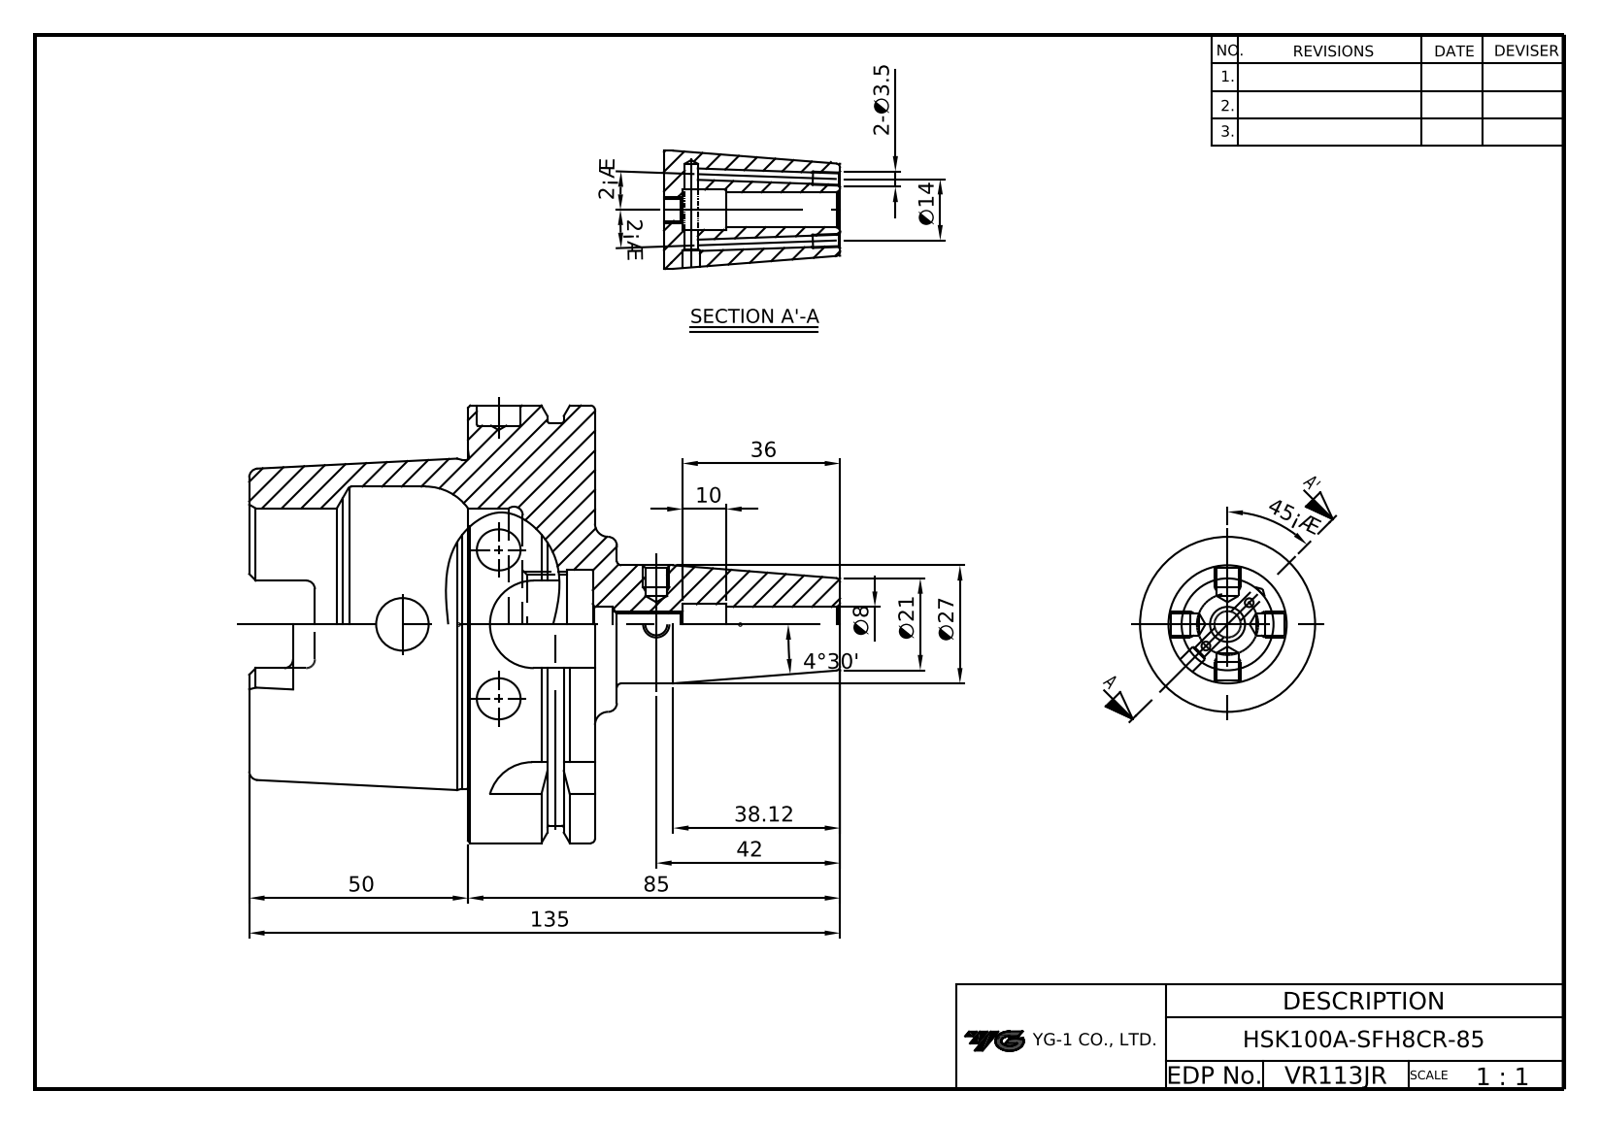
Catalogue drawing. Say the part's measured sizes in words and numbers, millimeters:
The part is named "LO-HSK100A-SFH8CR-85". Its 3-D file was written by "Autodesk Inventor 2024 (AUTOMOTIVE_DESIGN)". It is 1 solid with 122 faces: 39 planar, 36 cylindrical and 47 other. Overall it measures 135 by 100 by 100 millimeters. Its volume is 282 689 cubic millimeters and its surface area 55 471 square millimeters. Round holes: 2 of diameter 2.46, 1 of diameter 4.92, 1 of diameter 8, 1 of diameter 9.2, 1 of diameter 10, 1 of diameter 12, 1 of diameter 22.38, 1 of diameter 25, 1 of diameter 53, 1 of diameter 63. Round bosses or shafts: 1 of diameter 100, 1 of diameter 92, 1 of diameter 75.41, 1 of diameter 27. Partial cylindrical surfaces (rounded edges, fillets, slot ends): 6 of radius 2, 4 of radius 4.88, 4 of radius 10. The main face-to-face distances are 29, 12.5, 16.5, 62.5, 50, 79, 78.5, 28.5, 16, 0.5.
